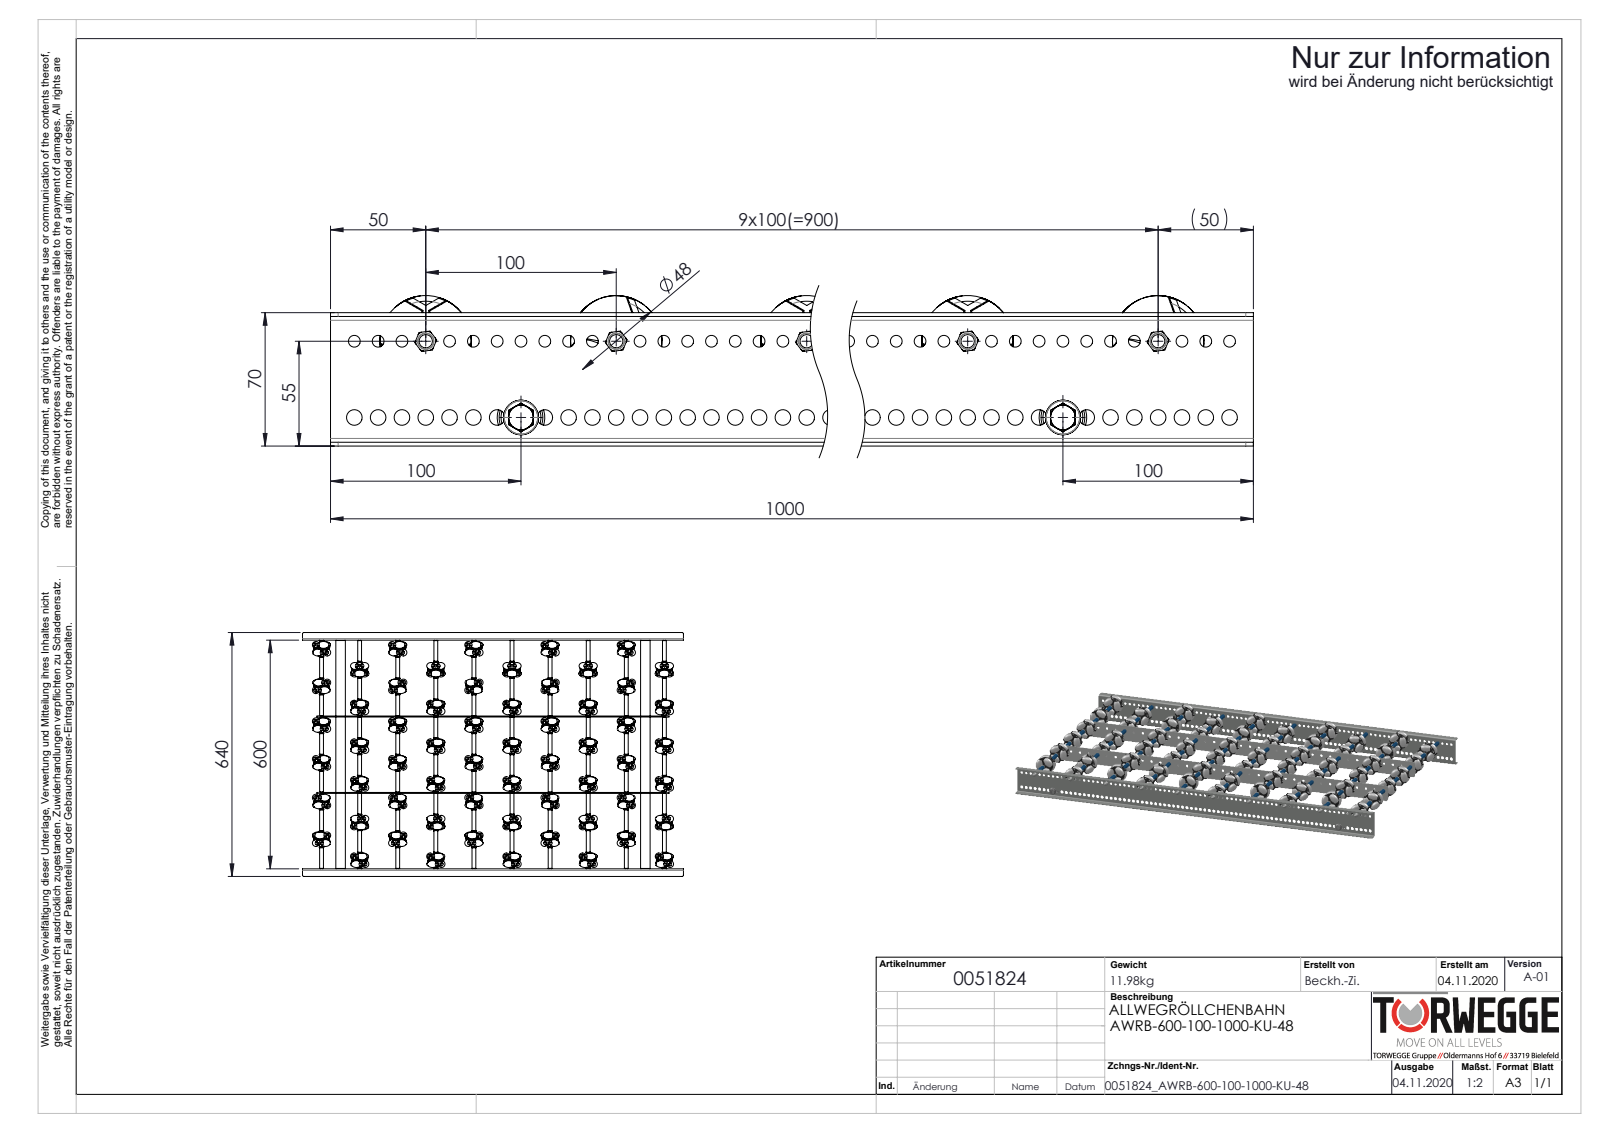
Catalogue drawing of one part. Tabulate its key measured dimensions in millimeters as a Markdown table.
| quantity | value |
| --- | --- |
| part name | AWR48_Stift; AWR48_Halter; 0036819_SICHERUNGS-HUTMUTTER-DIN986-M6; 0051824 (+8 more) |
| STEP written by | SolidWorks 2020 (AUTOMOTIVE_DESIGN) |
| units | millimeters |
| bodies | 1004 solids, 18060 faces (6192 planar, 7184 cylindrical, 4684 other) |
| overall size | 1000 × 640 × 79 |
| volume | 3 653 000 mm³ |
| surface area | 2 571 000 mm² |
| round holes (diameter × count) | 3.7 × 360, 4.2 × 360, 6.2 × 79, 8.2 × 79, 6.5 × 37, 4.92 × 10, 8.4 × 10, 6.8 × 2, 21 × 2 |
| round bosses / shafts (diameter × count) | 4 × 360, 3.7 × 308, 8 × 12, 47.1 × 10, 42 × 10, 11 × 10, 10 × 10, 7 × 10 |
| partial cylindrical surfaces (radius × count) | 4 × 8, 2 × 4, 5 × 4 |
| main face-to-face distances | 2, 602, 200.5, 2.5, 68, 600, 604, 398.4, 401.6, 201.1 |
| hole center spacings | 36.06, 36.05, 36.07, 100, 36.04, 200, 12.5, 25 |
